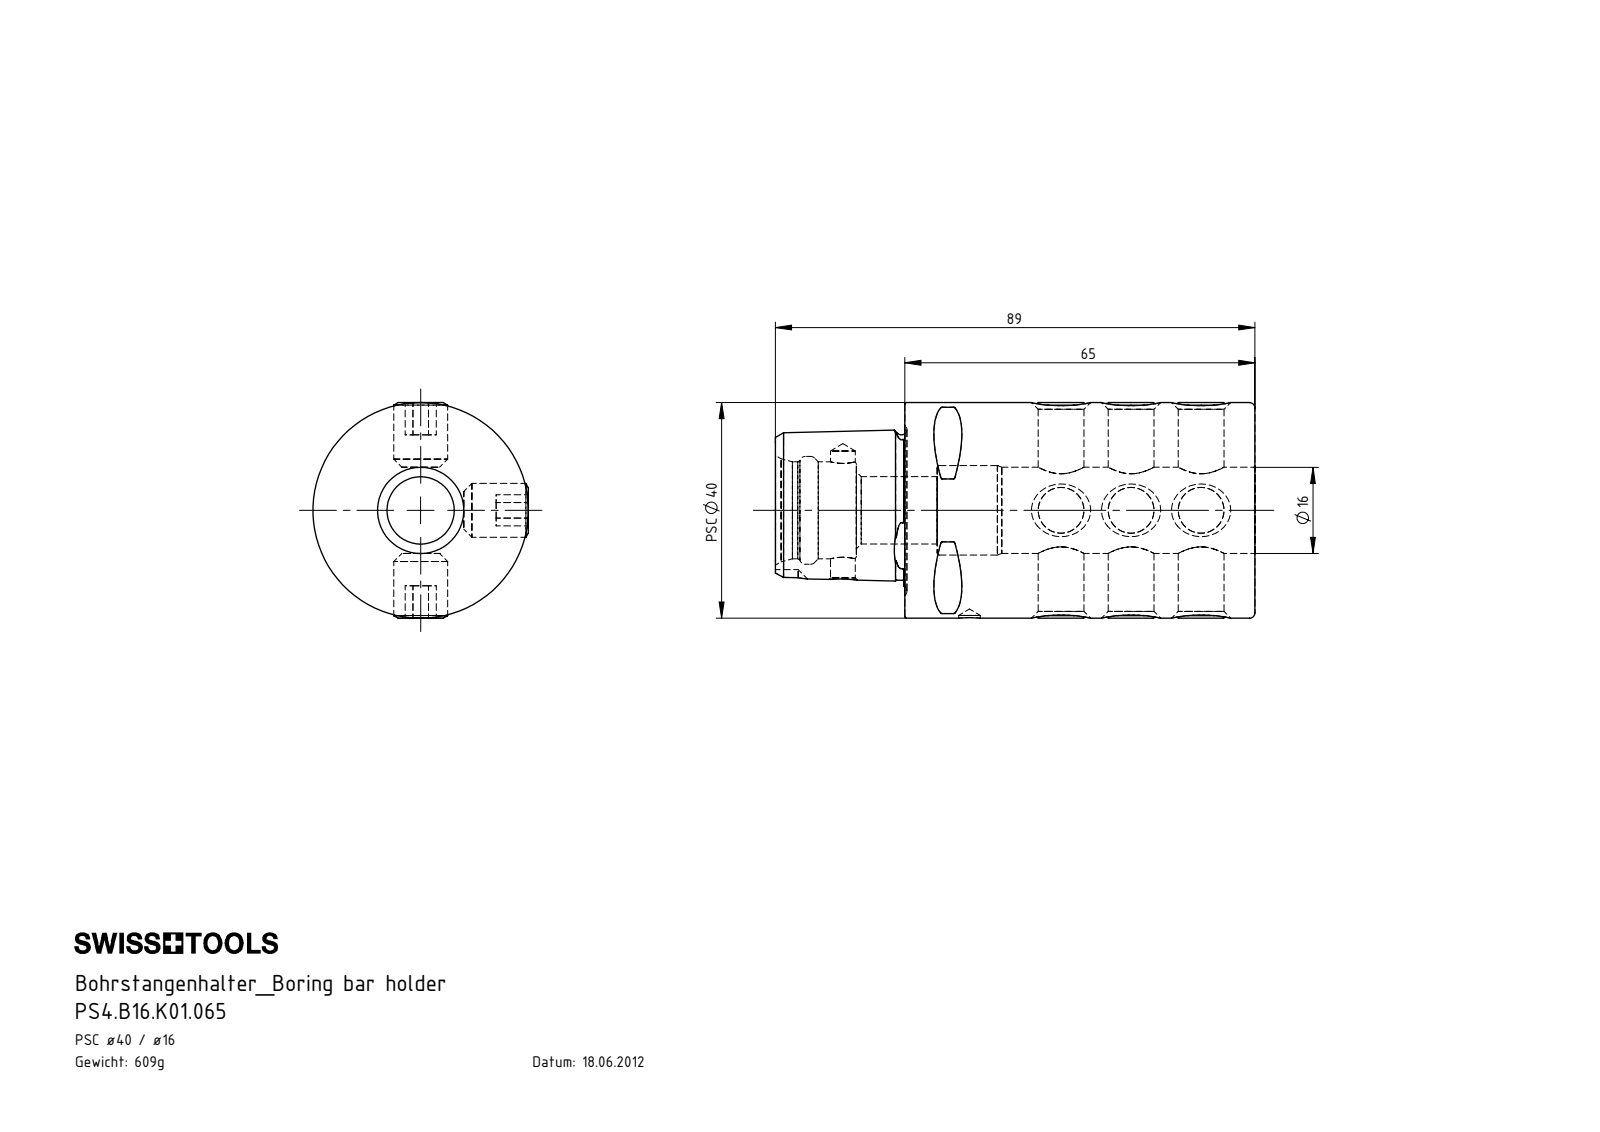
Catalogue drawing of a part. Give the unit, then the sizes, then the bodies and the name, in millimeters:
Units: millimetres
Overall size (bounding box): 89 × 40 × 40
Round holes (diameter × count): ⌀8.5 ×6, ⌀4 ×1, ⌀4.6 ×1, ⌀12.5 ×1, ⌀16 ×1, ⌀16.6 ×1, ⌀18 ×1, ⌀20 ×1
Round bosses / shafts (diameter × count): ⌀10 ×6, ⌀40 ×1
Partial cylindrical surfaces — rounded edges, fillets, slot ends (radius × count): R0.3 ×8, R3 ×1
Main face-to-face distances: 65, 6, 5, 6.5, 24, 89, 28, 12, 15, 22
Hole centre spacings: 13, 26, 17, 23.5, 30, 40.5, 43, 53.5
Volume: 77 574 mm³ · Surface area: 24 068 mm²
Bodies: 10 solids, 324 faces (101 planar, 65 cylindrical, 158 other)
Part name (STEP PRODUCT): ISO 4026 - M10 x 12_PreviewCfg; PS4.B16.K01.065; PS4-B16.K01.065_A
STEP written by: SolidWorks 2017 (AUTOMOTIVE_DESIGN)
